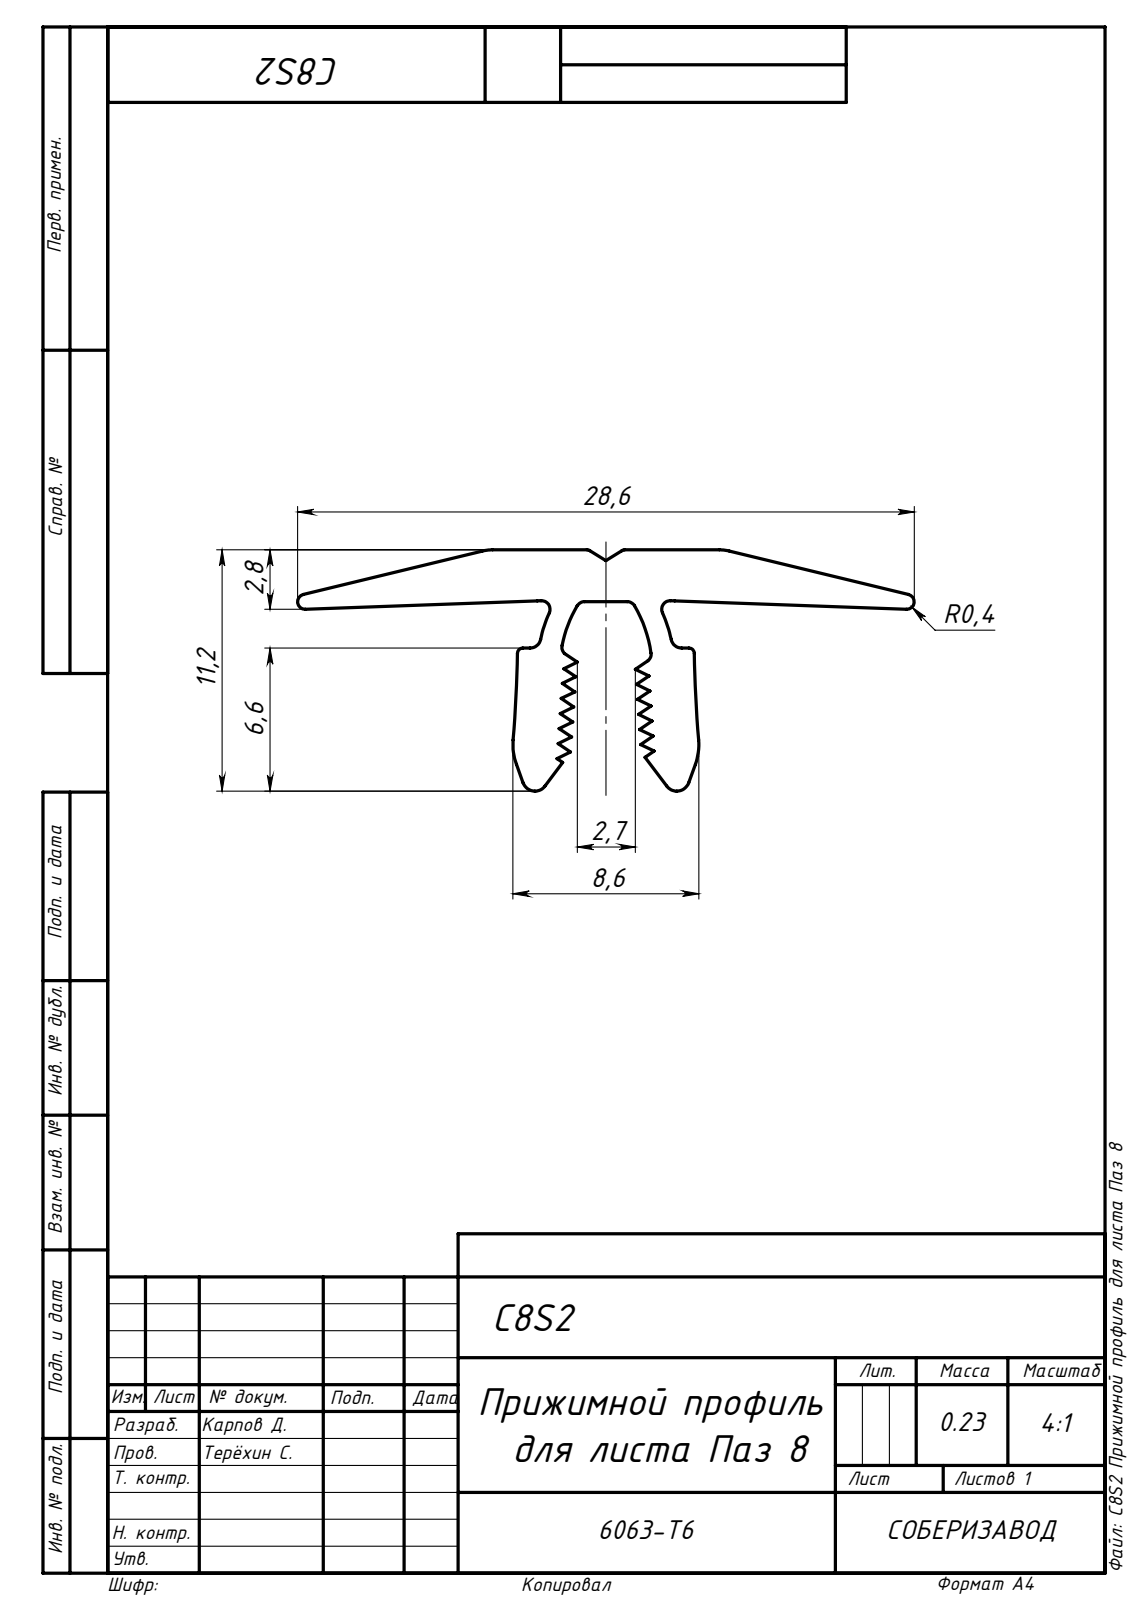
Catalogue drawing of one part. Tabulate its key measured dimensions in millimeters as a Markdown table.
| quantity | value |
| --- | --- |
| part name | C8S2 Прижимной профиль для листа Паз 8 |
| STEP written by | SolidWorks 2018 (AUTOMOTIVE_DESIGN) |
| units | millimeters |
| bodies | 1 solid, 80 faces (47 planar, 33 cylindrical, 0 other) |
| overall size | 1000 × 28.6 × 11.2 |
| volume | 86 942 mm³ |
| surface area | 104 669 mm² |
| partial cylindrical surfaces (radius × count) | 0.4 × 6, 0.25 × 4, 0.6 × 4, 6 × 4, 0.35 × 2, 0.5 × 2, 2 × 2, 2.7 × 2 |
| main face-to-face distances | 1.21, 0.61, 1.82, 0.6, 2.42, 3.03, 1.22, 2.43, 1.81, 2.4 |
